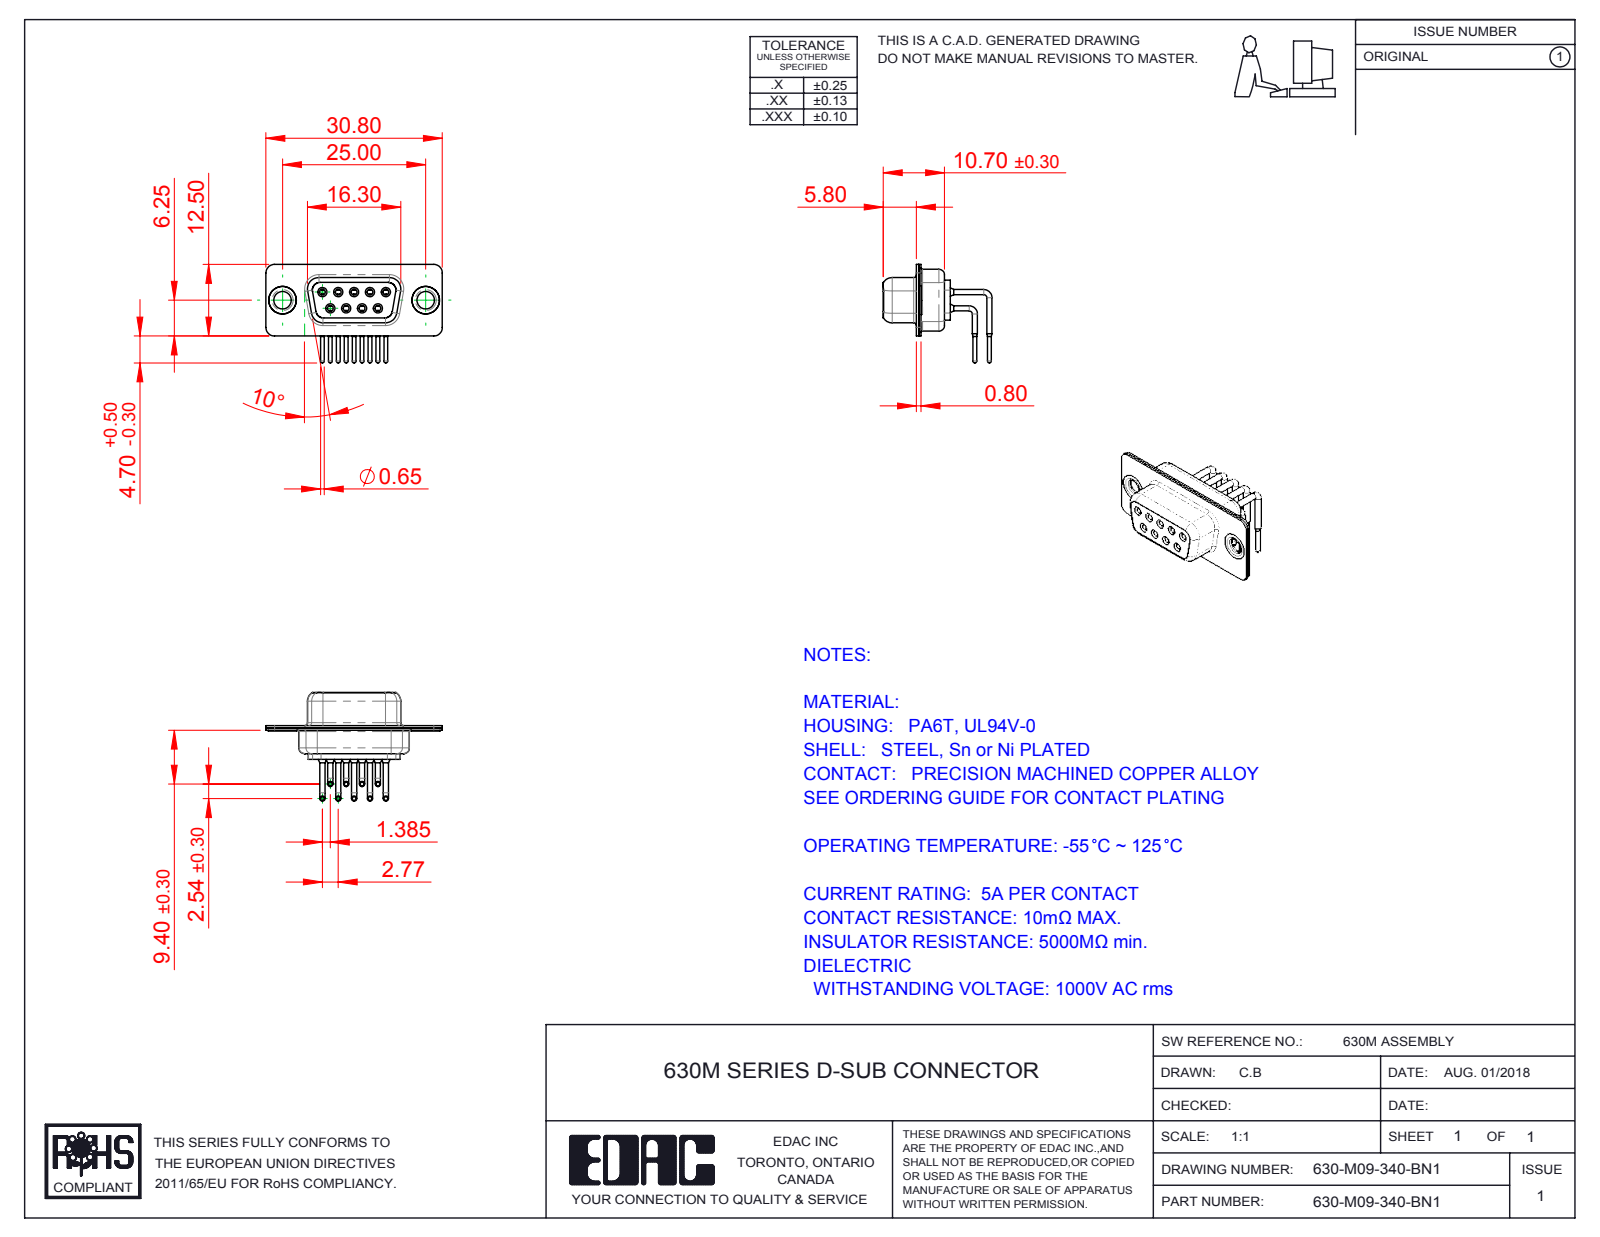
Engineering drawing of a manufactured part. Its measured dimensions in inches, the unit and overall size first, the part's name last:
Units: inches
Overall size (bounding box): 1.213 × 0.748 × 0.677
Round holes (diameter × count): ⌀0.039 ×9, ⌀0.043 ×9, ⌀0.067 ×9, ⌀0.071 ×9, ⌀0.079 ×9, ⌀0.12 ×2, ⌀0.157 ×2, ⌀0.189 ×2
Round bosses / shafts (diameter × count): ⌀0.035 ×18, ⌀0.063 ×9, ⌀0.059 ×9, ⌀0.026 ×9, ⌀0.197 ×2, ⌀0.193 ×2, ⌀0.14 ×2
Partial cylindrical surfaces — rounded edges, fillets, slot ends (radius × count): R0.059 ×16, R0.079 ×12, R0.053 ×8, R0.063 ×8, R0.01 ×4, R0.02 ×4, R0.024 ×4, R0.026 ×4
Main face-to-face distances: 0.016, 0.031, 0.057, 0.352, 0.091, 0.244, 0.335, 0.075, 0.033, 0.368
Hole centre spacings: 0.124, 0.109, 0.218, 0.198, 0.198, 0.327, 0.28, 0.294
Volume: 0.103 in³ · Surface area: 6.96 in²
Bodies: 14 solids, 730 faces (202 planar, 328 cylindrical, 200 other)
Part name (STEP PRODUCT): 630M Contact Row 1; 630M Housing_09 Contacts; 630M Shell Rear_09 Contacts; 630M Contact Row 2 (+3 more)
STEP written by: SolidWorks 2016 (CONFIG_CONTROL_DESIGN)
